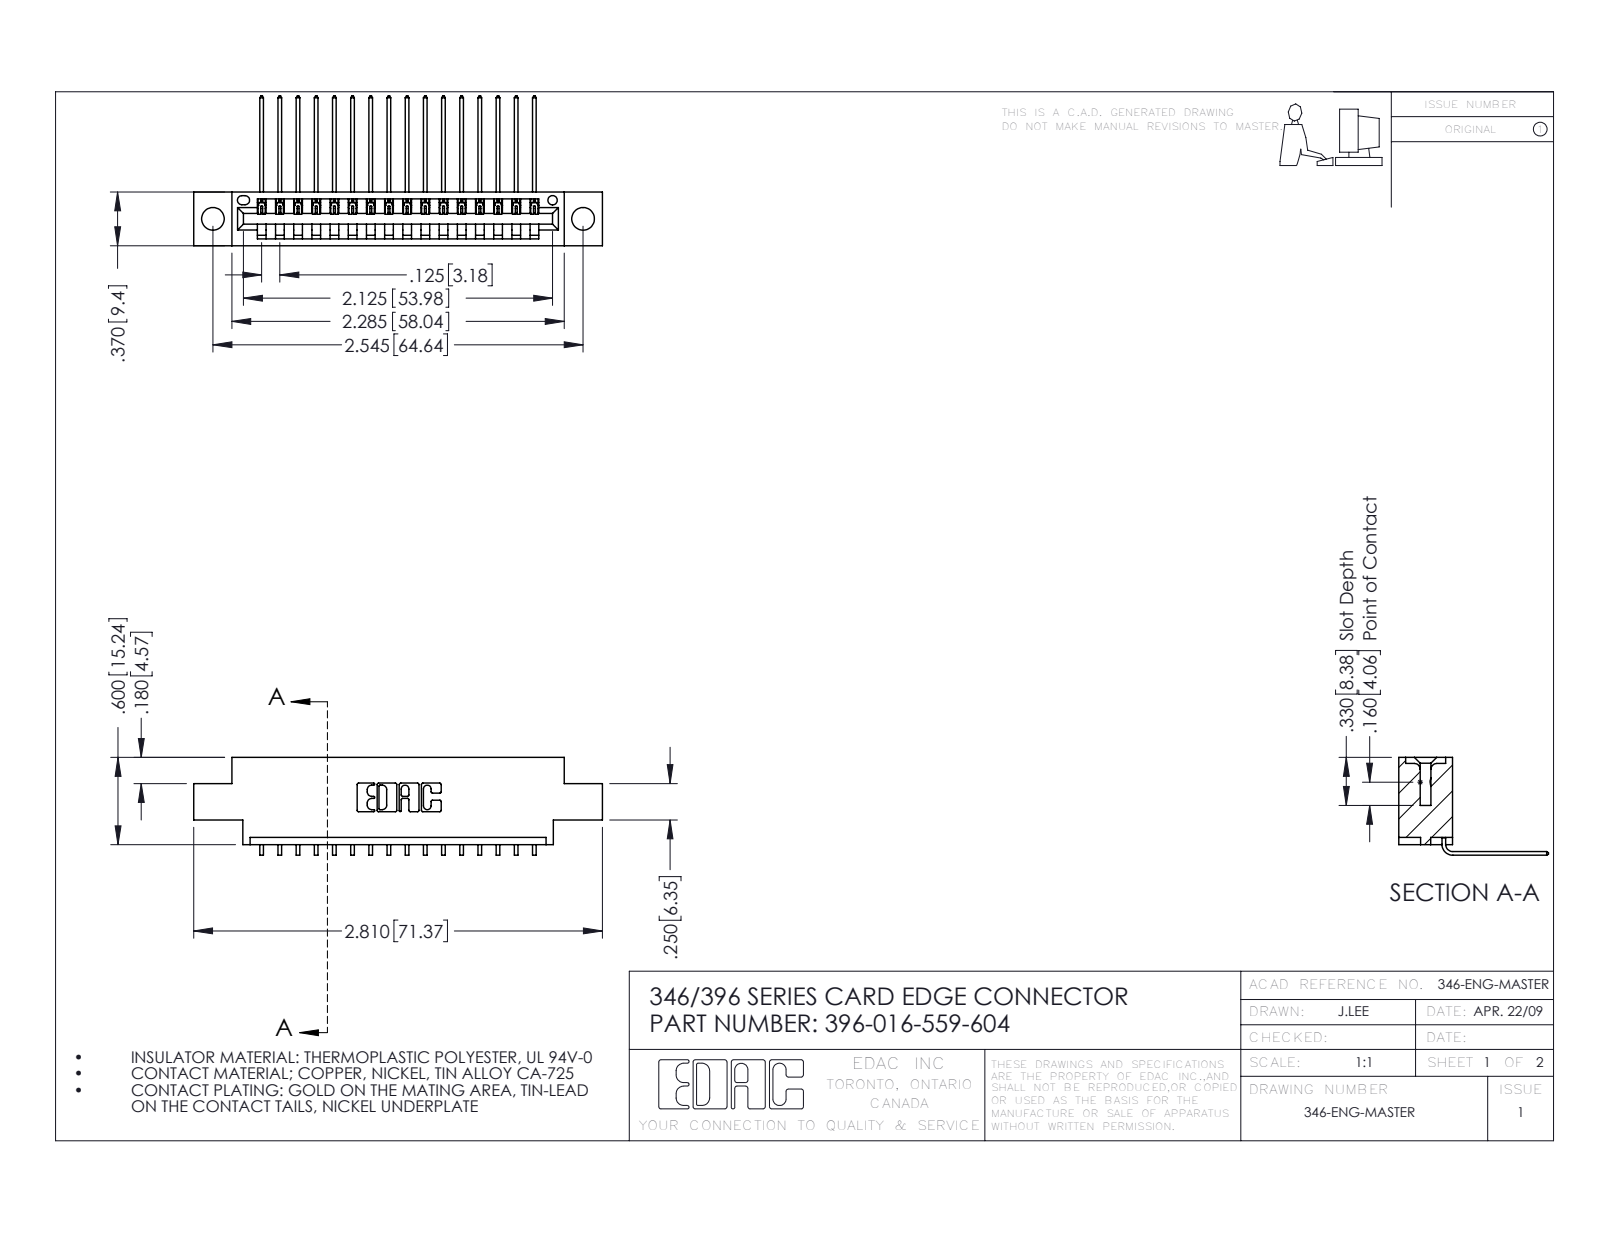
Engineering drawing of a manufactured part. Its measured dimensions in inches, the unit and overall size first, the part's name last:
Units: inches
Overall size (bounding box): 2.81 × 1.03 × 0.673
Round holes (diameter × count): ⌀0.156 ×2, ⌀0.064 ×1
Partial cylindrical surfaces — rounded edges, fillets, slot ends (radius × count): R0.006 ×32, R0.01 ×22, R0.007 ×6, R0.031 ×6, R0.026 ×3, R0.031 ×2, R0.04 ×2, R0.014 ×1
Main face-to-face distances: 0.048, 0.37, 0.322, 0.25, 0.025, 0.072, 0.148, 0.222, 0.1, 0.174
Hole centre spacings: 0.246, 2.338, 2.545
Volume: 0.394 in³ · Surface area: 12.53 in²
Bodies: 17 solids, 1086 faces (752 planar, 334 cylindrical, 0 other)
Part name (STEP PRODUCT): 345-292-001_558 559 Tail - 1; 346 Part_0.170 Offset - 0.156 Dia-TH; 396-016-559-604
STEP written by: SolidWorks 2016 (CONFIG_CONTROL_DESIGN)
